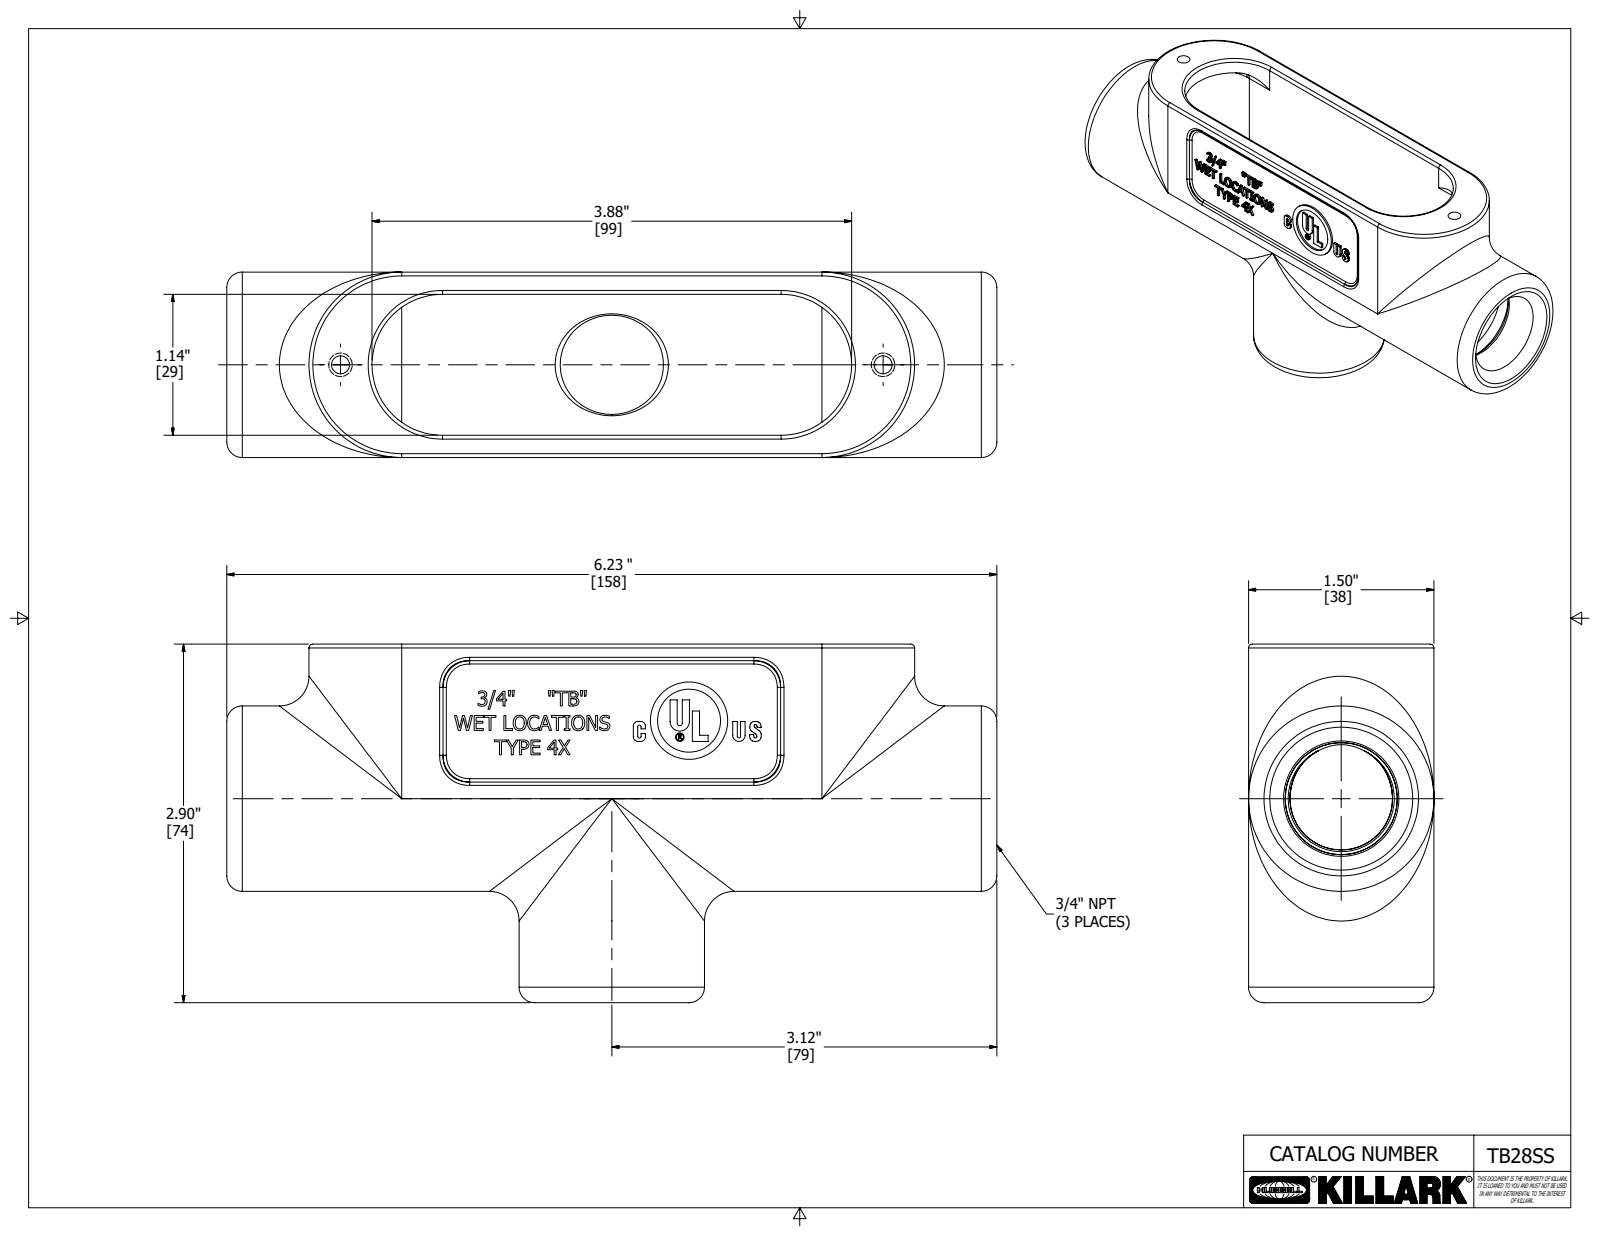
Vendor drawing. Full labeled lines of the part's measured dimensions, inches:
Part name (STEP PRODUCT): TB28SS
STEP written by: Autodesk Inventor 2020 (AUTOMOTIVE_DESIGN)
Units: inches
Bodies: 1 solid, 557 faces (323 planar, 80 cylindrical, 154 other)
Overall size (bounding box): 6.23 × 2.9 × 1.5
Volume: 7.728 in³ · Surface area: 71.3 in²
Round holes (diameter × count): ⌀0.145 ×2, ⌀1.055 ×2, ⌀0.058 ×1, ⌀0.509 ×1
Round bosses / shafts (diameter × count): ⌀1.5 ×2, ⌀0.625 ×1, ⌀0.069 ×1
Partial cylindrical surfaces — rounded edges, fillets, slot ends (radius × count): R0.031 ×13, R0.57 ×5, R0.038 ×4, R0.25 ×4, R0.013 ×2, R0.013 ×2, R0.125 ×2, R0.75 ×2
Main face-to-face distances: 0.18, 1.32, 1.14, 0.149, 1.289, 1.469, 0.031, 1.5, 0.02, 0.169
Hole centre spacings: 2.195, 0.153, 4.39
